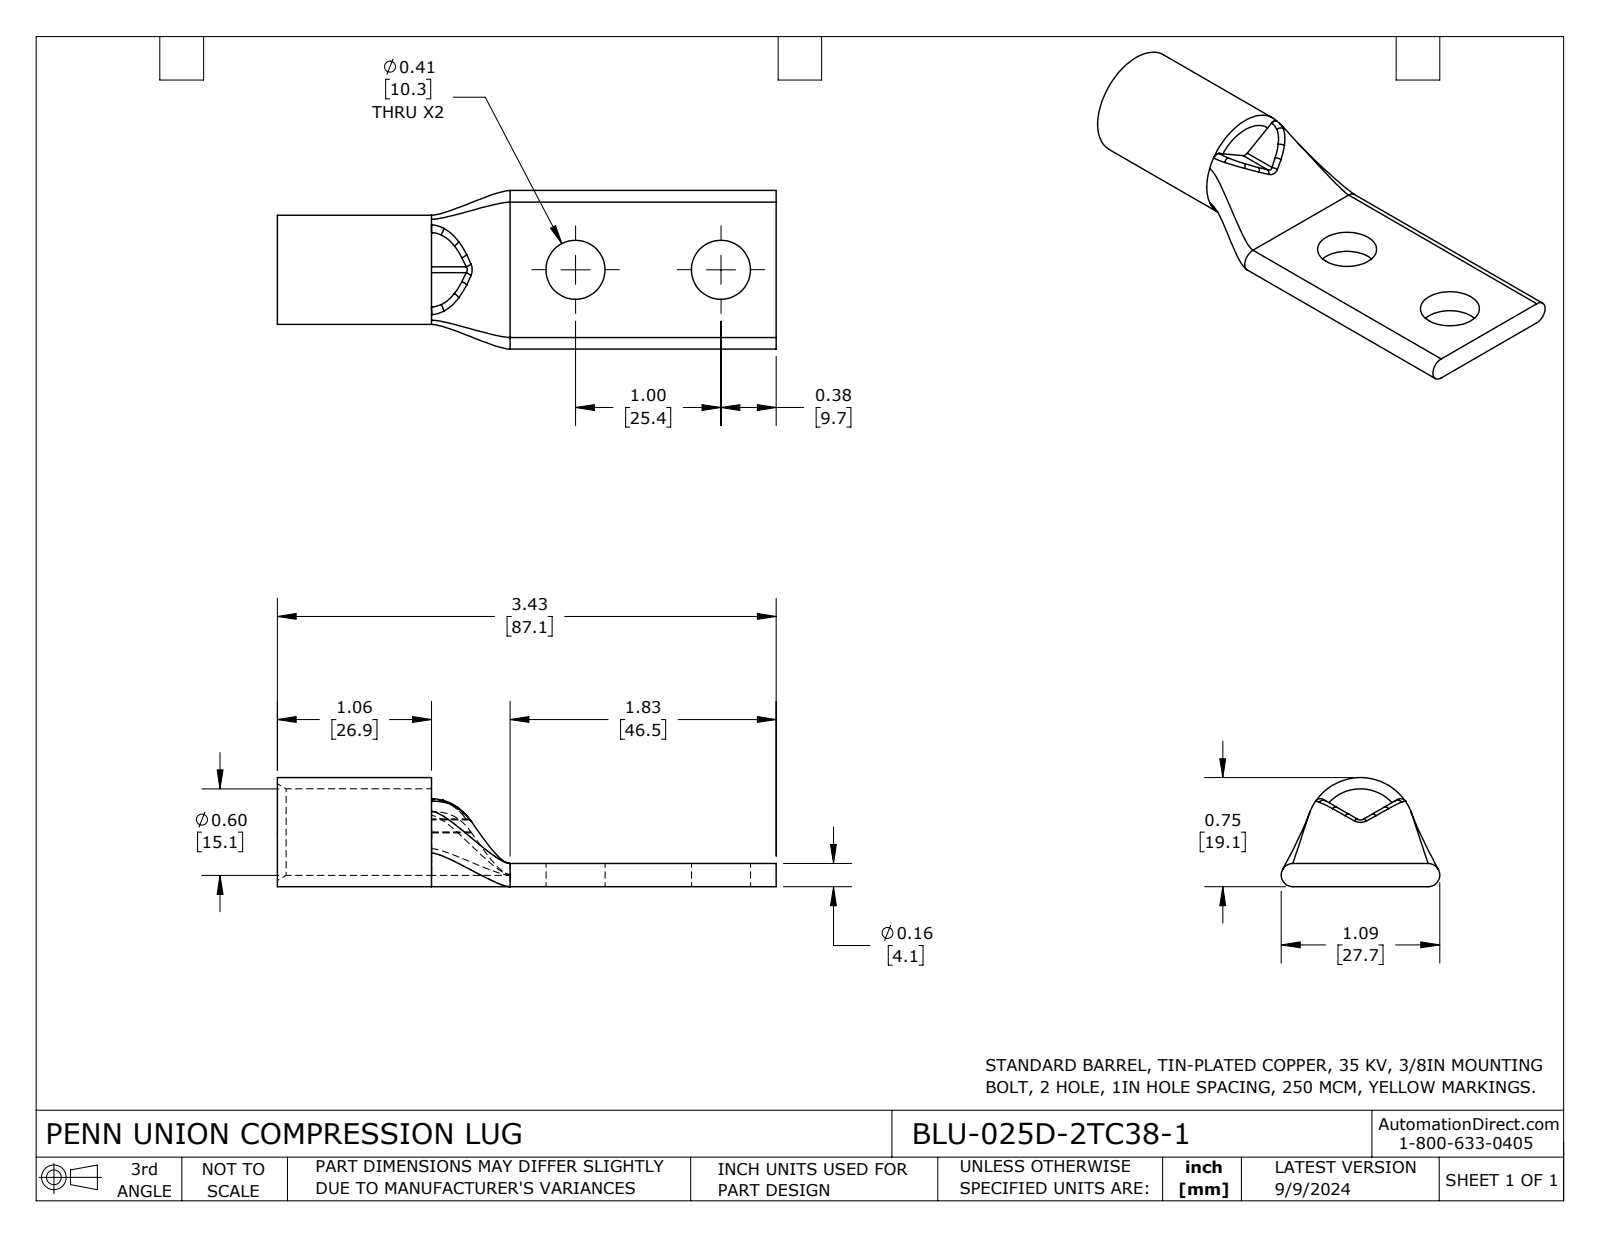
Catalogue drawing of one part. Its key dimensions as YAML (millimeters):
part_name: "BLU-025D-2TC38-1"
step_written_by: "SolidWorks 2023 (CONFIG_CONTROL_DESIGN)"
units: millimeters
bodies: {solids: 1, faces: 45, planar: 11, cylindrical: 13, other: 21}
overall_size: [87.1, 27.7, 19.1]
volume: 8570
surface_area: 7471
round_holes:
  - {diameter: 10.3, count: 2}
  - {diameter: 15.1, count: 1}
round_bosses_or_shafts:
  - {diameter: 19.1, count: 1}
partial_cylinders:
  - {radius: 1, count: 2}
  - {radius: 2, count: 2}
face_to_face_distances: [4.1, 87.1, 2, 26.9, 60.2, 40.6, 13.7, 46.5]
hole_center_spacings: [25.4]
